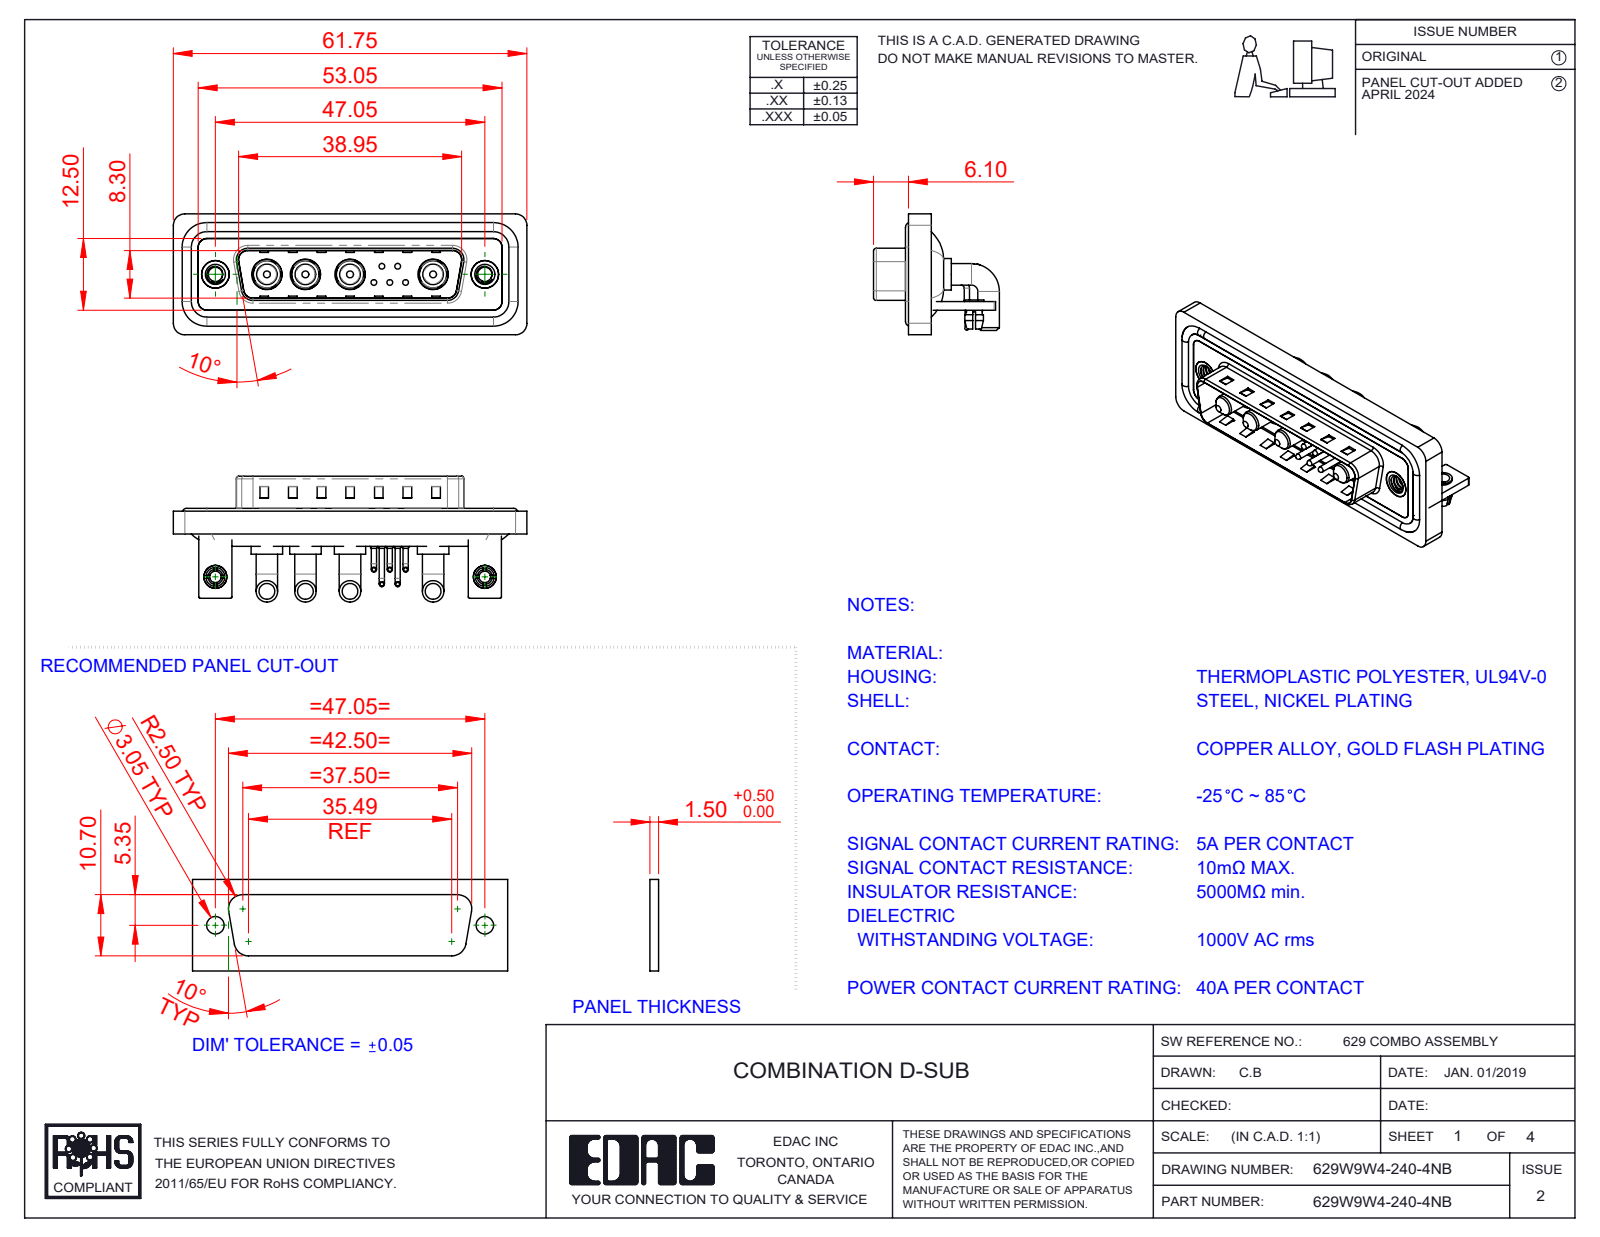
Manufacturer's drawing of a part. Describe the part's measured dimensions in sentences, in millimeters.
The part is named "629Combo Shell Front_25 Contacts; 629Combo Waterproof Housing_25 Contacts; 629W9W4-140-4NB; Power Pin_40A RA (+7 more)". Its 3-D file was written by "SolidWorks 2023 (CONFIG_CONTROL_DESIGN)". It is 24 solids with 1335 faces: 637 planar, 502 cylindrical and 196 other. Overall it measures 61.75 by 21.98 by 21.1 millimeters. Its volume is 8 304 cubic millimeters and its surface area 13 351 square millimeters. Round holes: 7 of diameter 2, 5 of diameter 0.75, 5 of diameter 1.6, 4 of diameter 2.5, 4 of diameter 4.85, 4 of diameter 5.3, 2 of diameter 3.2, 2 of diameter 4, 2 of diameter 4.8, 2 of diameter 5. Round bosses or shafts: 10 of diameter 0.9, 8 of diameter 3.75, 5 of diameter 1.5, 5 of diameter 1, 5 of diameter 0.65, 4 of diameter 5.5, 4 of diameter 5.2, 4 of diameter 4.75. Partial cylindrical surfaces (rounded edges, fillets, slot ends): 19 of radius 2, 18 of radius 1.5, 16 of radius 0.25, 9 of radius 0.5, 8 of radius 1.6, 5 of radius 1.01, 4 of radius 0.6, 4 of radius 0.65. The main face-to-face distances are 0.4, 1.5, 0.8, 2.9, 2.1, 1.1, 3.7, 4.1, 4.5, 1.6. The hole center spacings are 3.16, 2.77, 5.04, 14.5, 47.05, 2.78, 4.4, 4.41.
